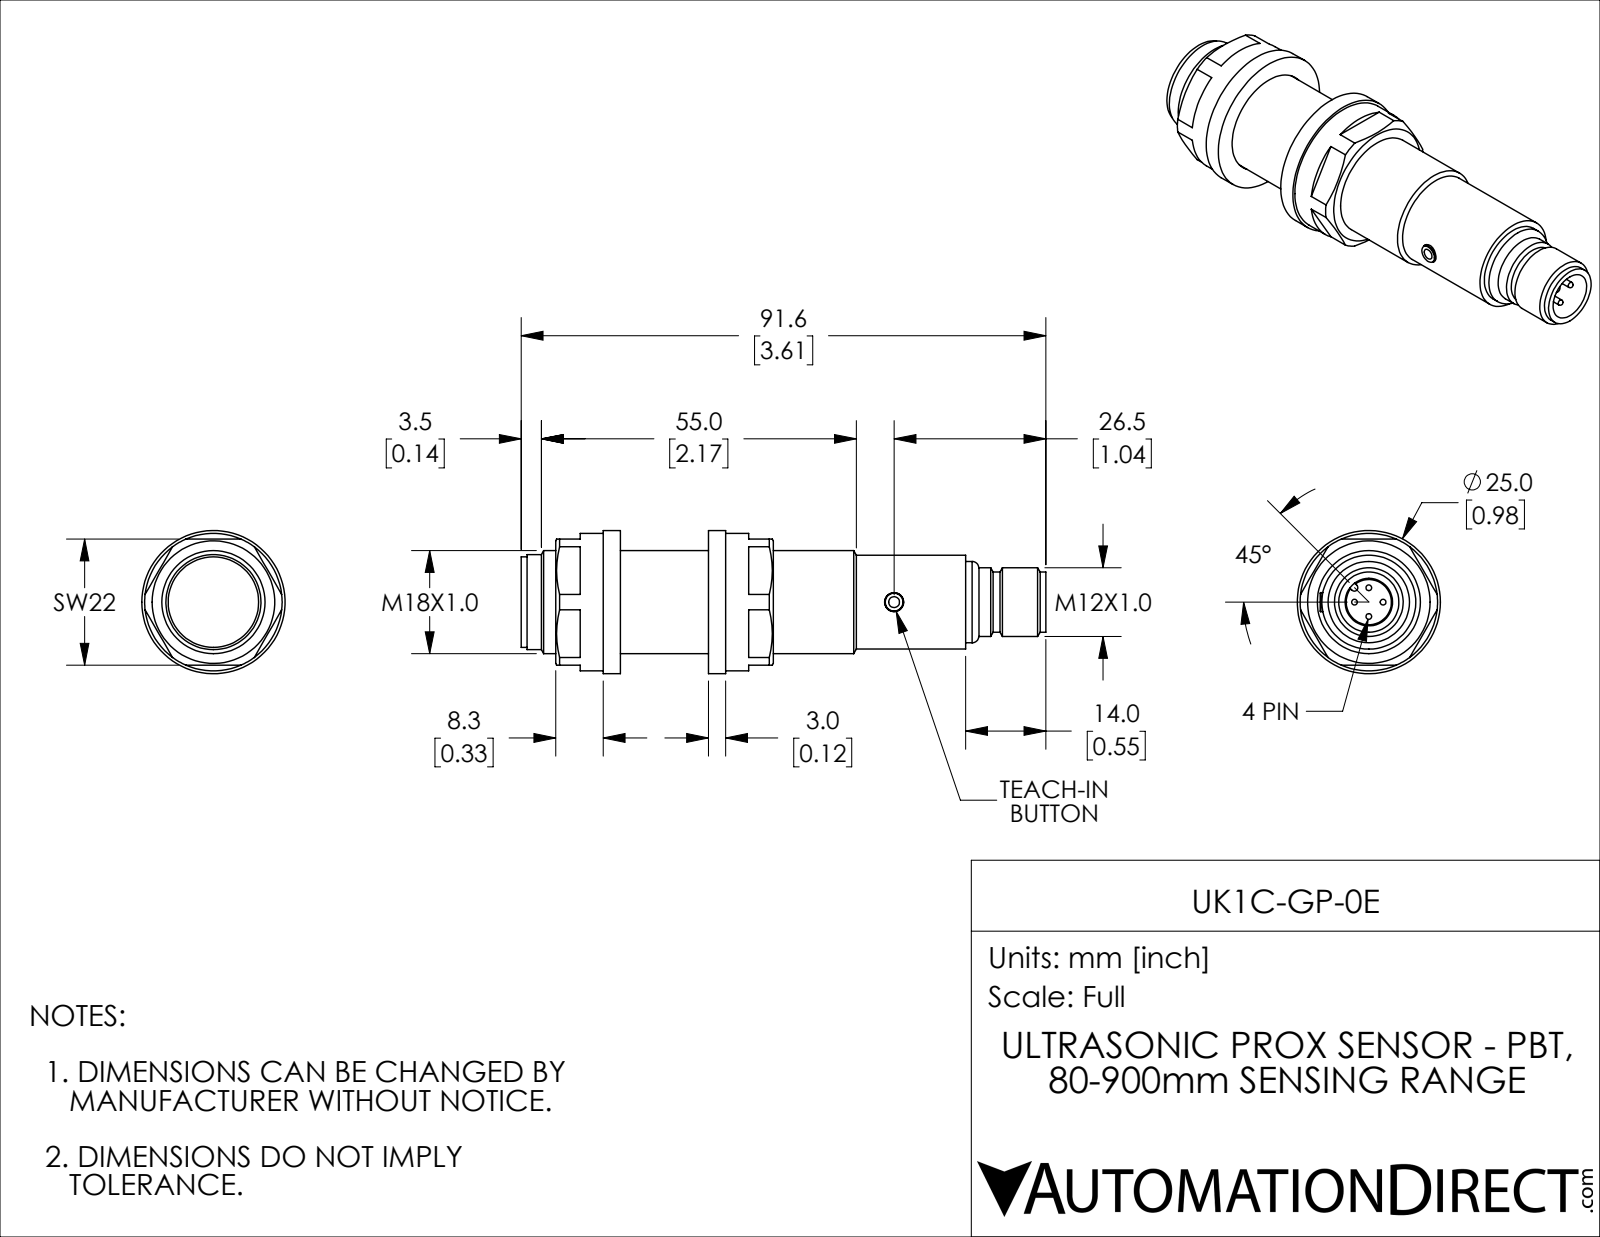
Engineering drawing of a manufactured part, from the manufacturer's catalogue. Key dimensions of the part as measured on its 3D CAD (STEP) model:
Part name (STEP PRODUCT): UK1C-GP-0E
STEP written by: SolidWorks 2018 (AUTOMOTIVE_DESIGN)
Units: inches
Bodies: 6 solids, 123 faces (43 planar, 49 cylindrical, 31 other)
Overall size (bounding box): 3.606 × 0.984 × 0.984
Volume: 1.477 in³ · Surface area: 16.01 in²
Round holes (diameter × count): ⌀0.13 ×1, ⌀0.327 ×1, ⌀0.709 ×1, ⌀0.717 ×1
Round bosses / shafts (diameter × count): ⌀0.039 ×4, ⌀0.984 ×1, ⌀0.945 ×1, ⌀0.654 ×1, ⌀0.646 ×1, ⌀0.622 ×1, ⌀0.559 ×1, ⌀0.472 ×1
Partial cylindrical surfaces — rounded edges, fillets, slot ends (radius × count): R0.024 ×1
Main face-to-face distances: 0.118, 0.724, 0.843, 0.606, 0.866, 0.327, 0.445, 1.051, 1.169, 0.563
